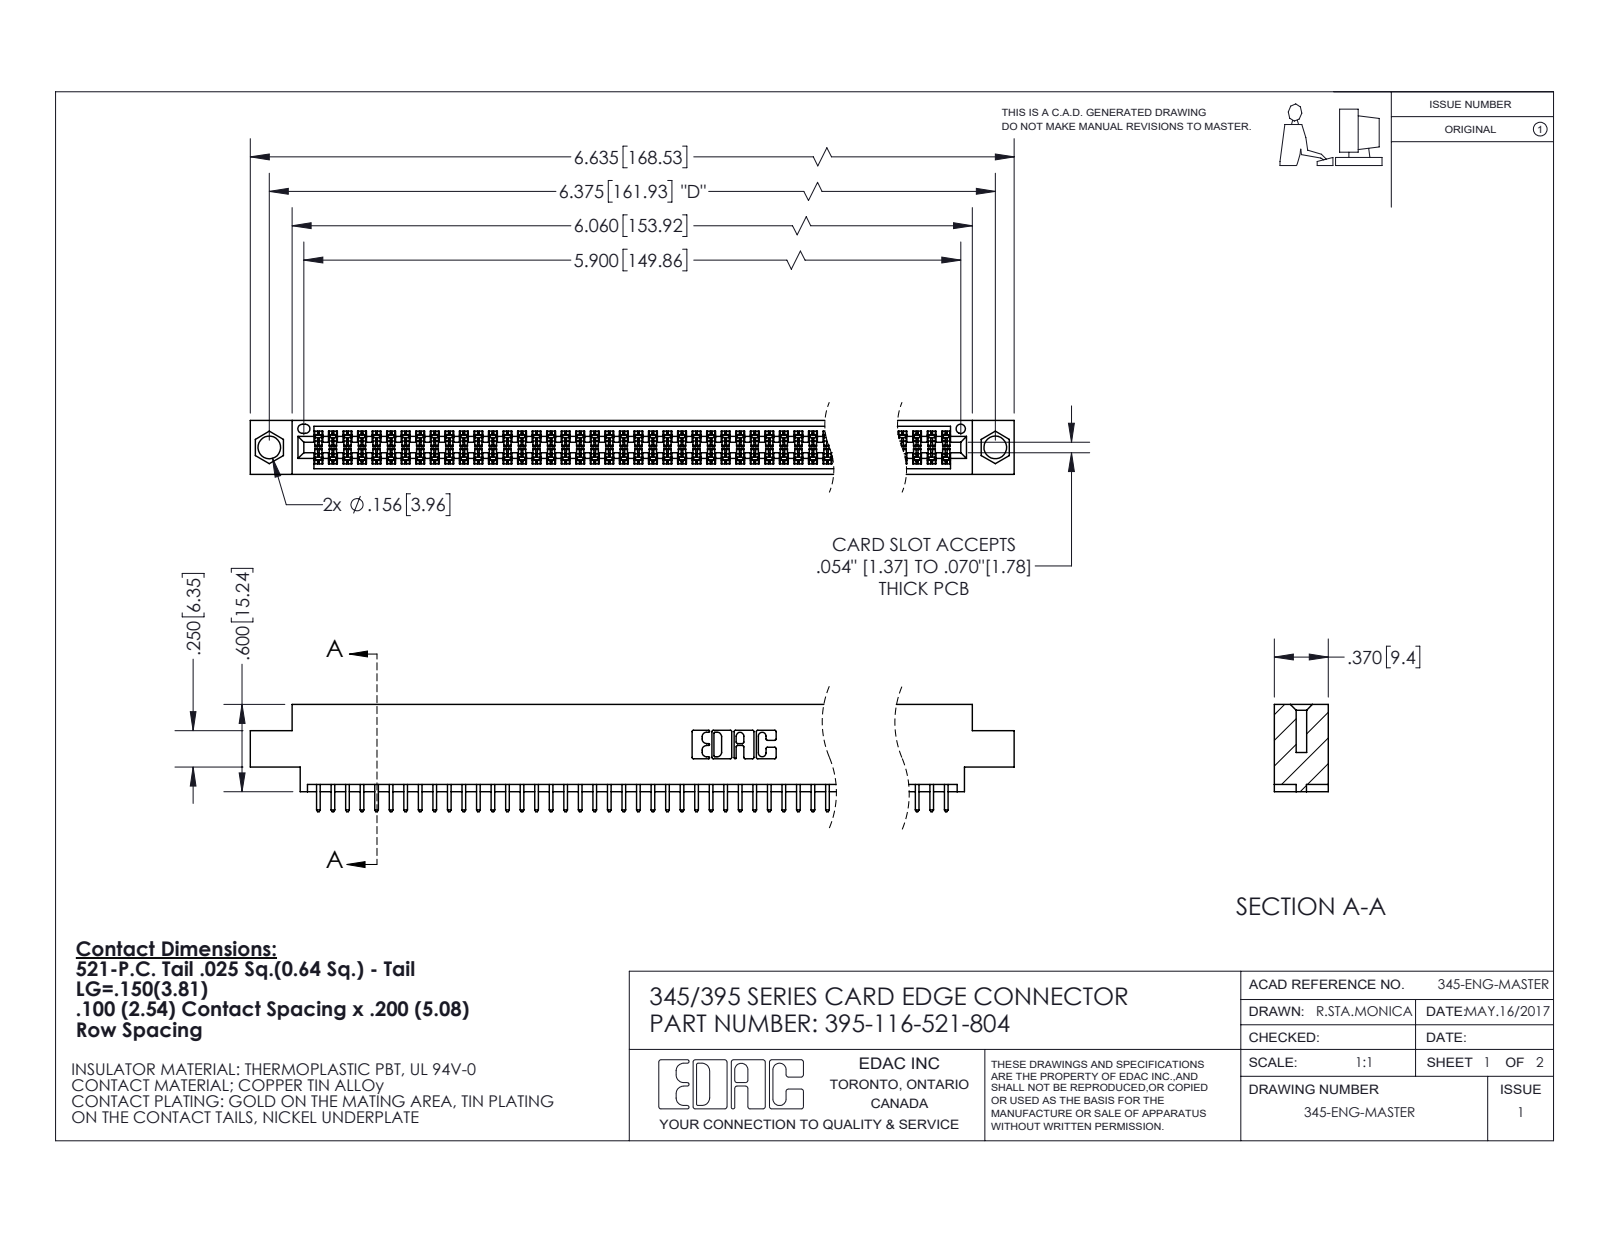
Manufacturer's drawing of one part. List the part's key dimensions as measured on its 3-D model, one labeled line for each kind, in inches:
Part name (STEP PRODUCT): 345-292-001_345-293-121; 345 Part_0.170 Offset - 0.156 Dia-TI; 395-116-521-804
STEP written by: SolidWorks 2020 (CONFIG_CONTROL_DESIGN)
Units: inches
Bodies: 117 solids, 5944 faces (3926 planar, 2018 cylindrical, 0 other)
Overall size (bounding box): 6.635 × 0.737 × 0.37
Volume: 0.992 in³ · Surface area: 37.23 in²
Round holes (diameter × count): ⌀0.156 ×2, ⌀0.064 ×1
Partial cylindrical surfaces — rounded edges, fillets, slot ends (radius × count): R0.006 ×232, R0.01 ×116, R0.01 ×22, R0.007 ×6, R0.031 ×6, R0.026 ×3, R0.014 ×2, R0.019 ×2
Main face-to-face distances: 0.072, 0.298, 0.2, 0.37, 0.098, 0.272, 0.025, 0.225, 0.175, 0.149
Hole centre spacings: 0.27, 6.139, 6.375
